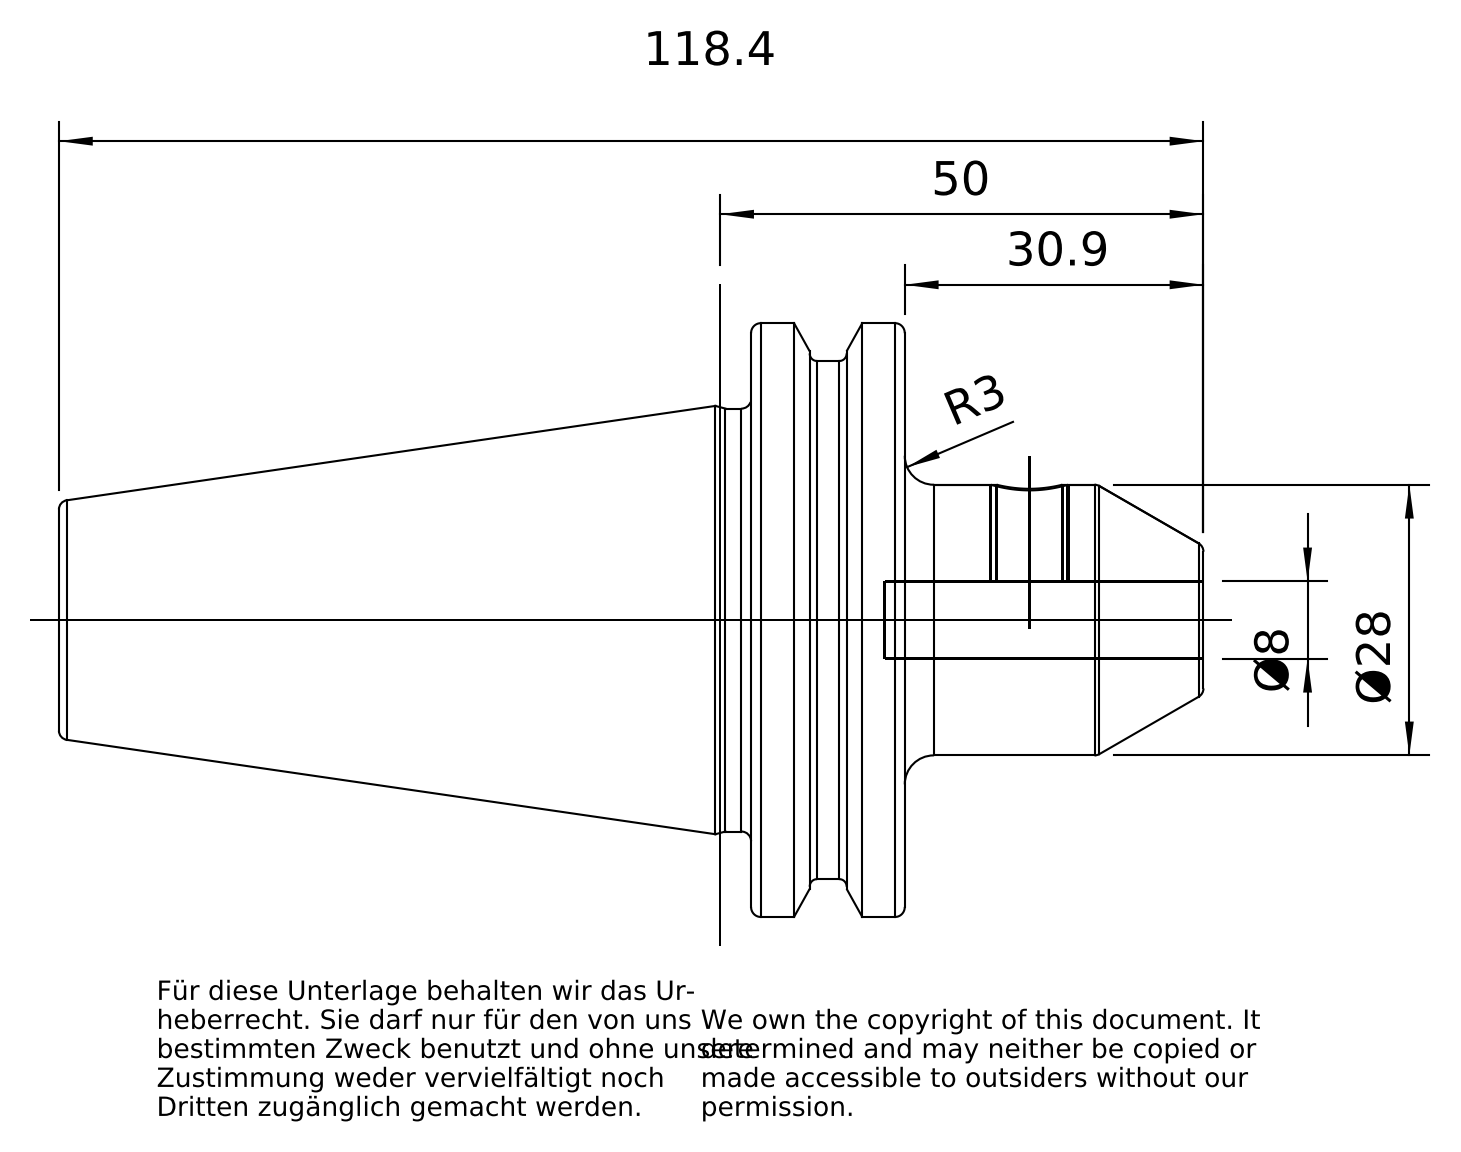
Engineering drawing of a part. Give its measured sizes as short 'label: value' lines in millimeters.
name: 40-300-08
written by: PRO/ENGINEER BY PARAMETRIC TECHNOLOGY CORPORATION, 2010430 (CONFIG_CONTROL_DESIGN)
unit: mm
bodies: 1 solid, 99 faces (21 planar, 28 cylindrical, 50 other)
size: 118.25 × 63.52 × 61.42
volume: 120 317 mm³; area: 23 298 mm²
holes: 2× ⌀8, 1× ⌀6.8, 1× ⌀13.84, 1× ⌀17.01, 1× ⌀17.5
bosses: 1× ⌀43.75, 1× ⌀28, 1× ⌀16.01
rounds: 1× R1.35, 1× R28, 1× R31.76
face distances: 15.85, 47.4, 16.2, 71.45, 87.3, 118.25, 46.8, 30.95, 6.5, 40.9
